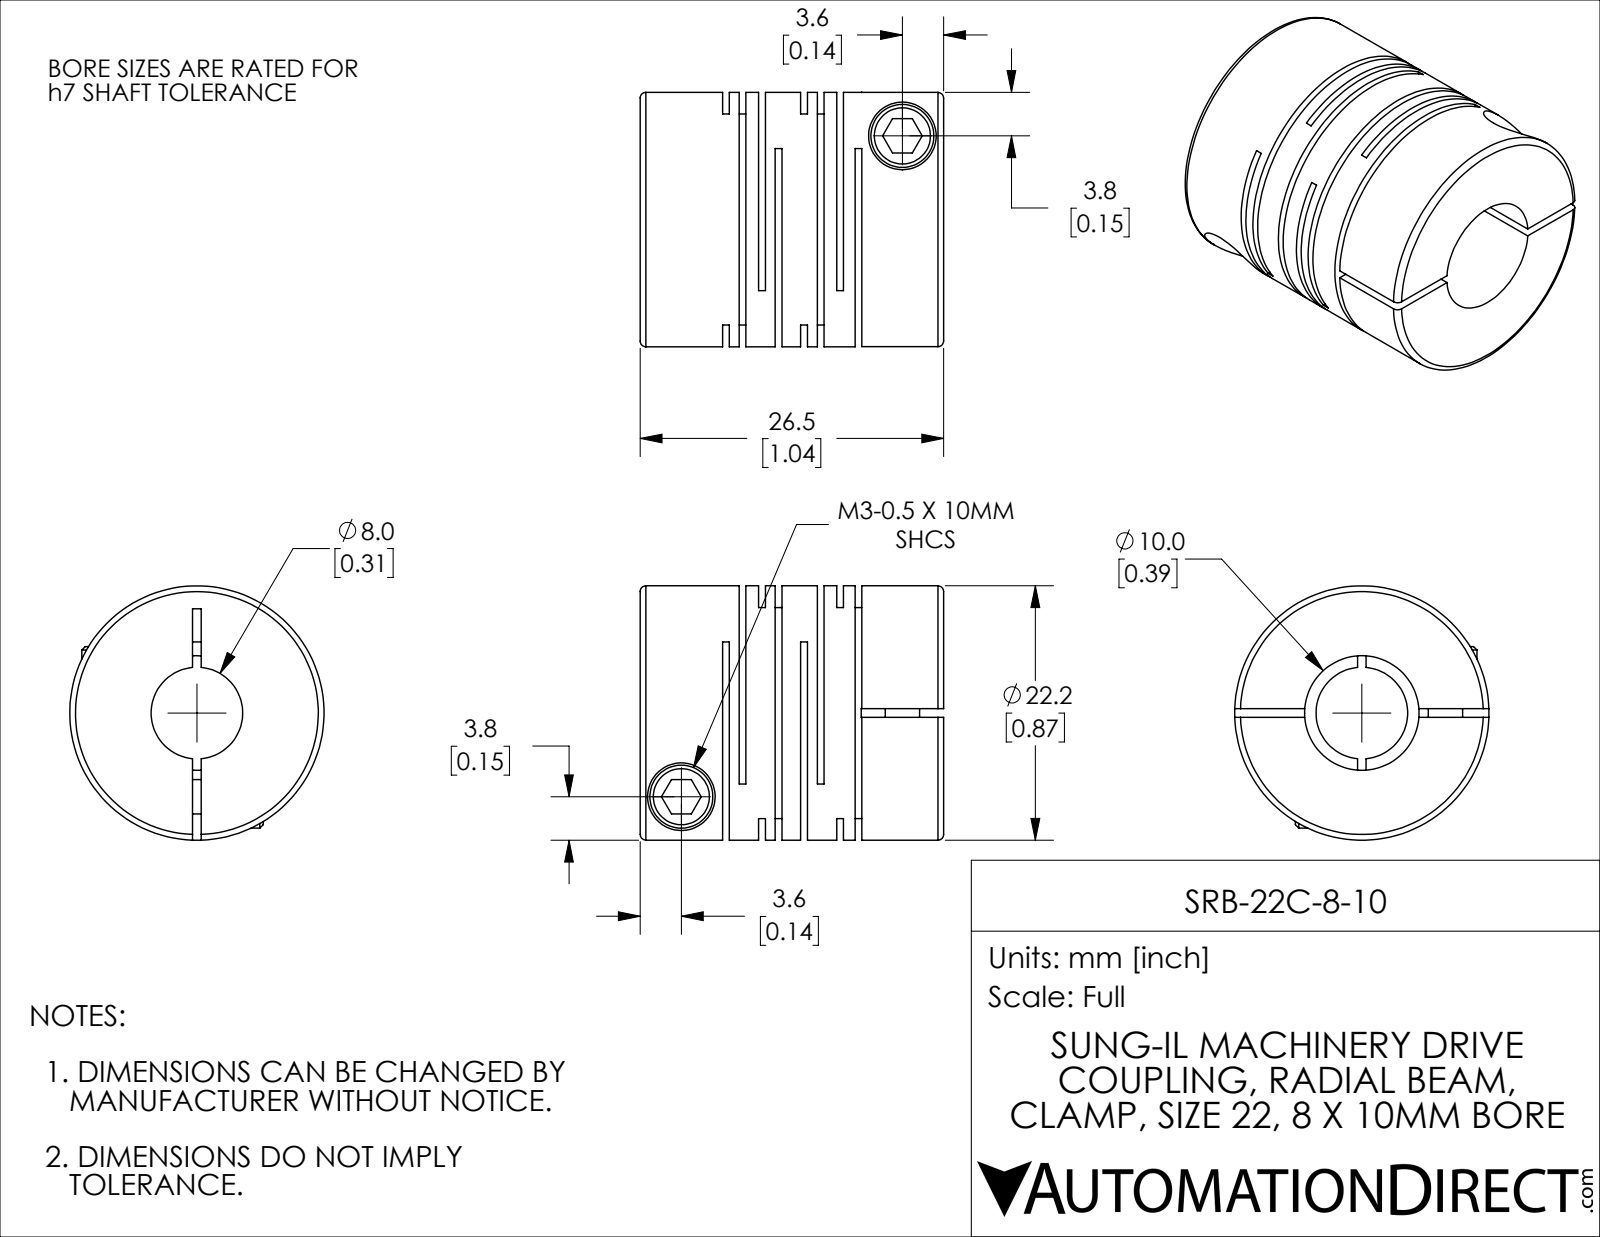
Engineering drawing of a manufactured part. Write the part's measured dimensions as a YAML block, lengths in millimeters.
part_name: "SRB-22C-8-10"
step_written_by: "SolidWorks 2021 (CONFIG_CONTROL_DESIGN)"
units: millimeters
bodies: {solids: 1, faces: 115, planar: 60, cylindrical: 42, other: 13}
overall_size: [26.5, 22.2, 22.2]
volume: 6909
surface_area: 7473
round_holes:
  - {diameter: 3, count: 2}
  - {diameter: 5.9, count: 2}
  - {diameter: 8, count: 1}
  - {diameter: 10, count: 1}
round_bosses_or_shafts:
  - {diameter: 5.5, count: 2}
  - {diameter: 22.2, count: 1}
face_to_face_distances: [0.59, 3.15, 6.82, 1.45, 5.37, 3.67, 1.7, 2.04, 3.74, 7.41]
